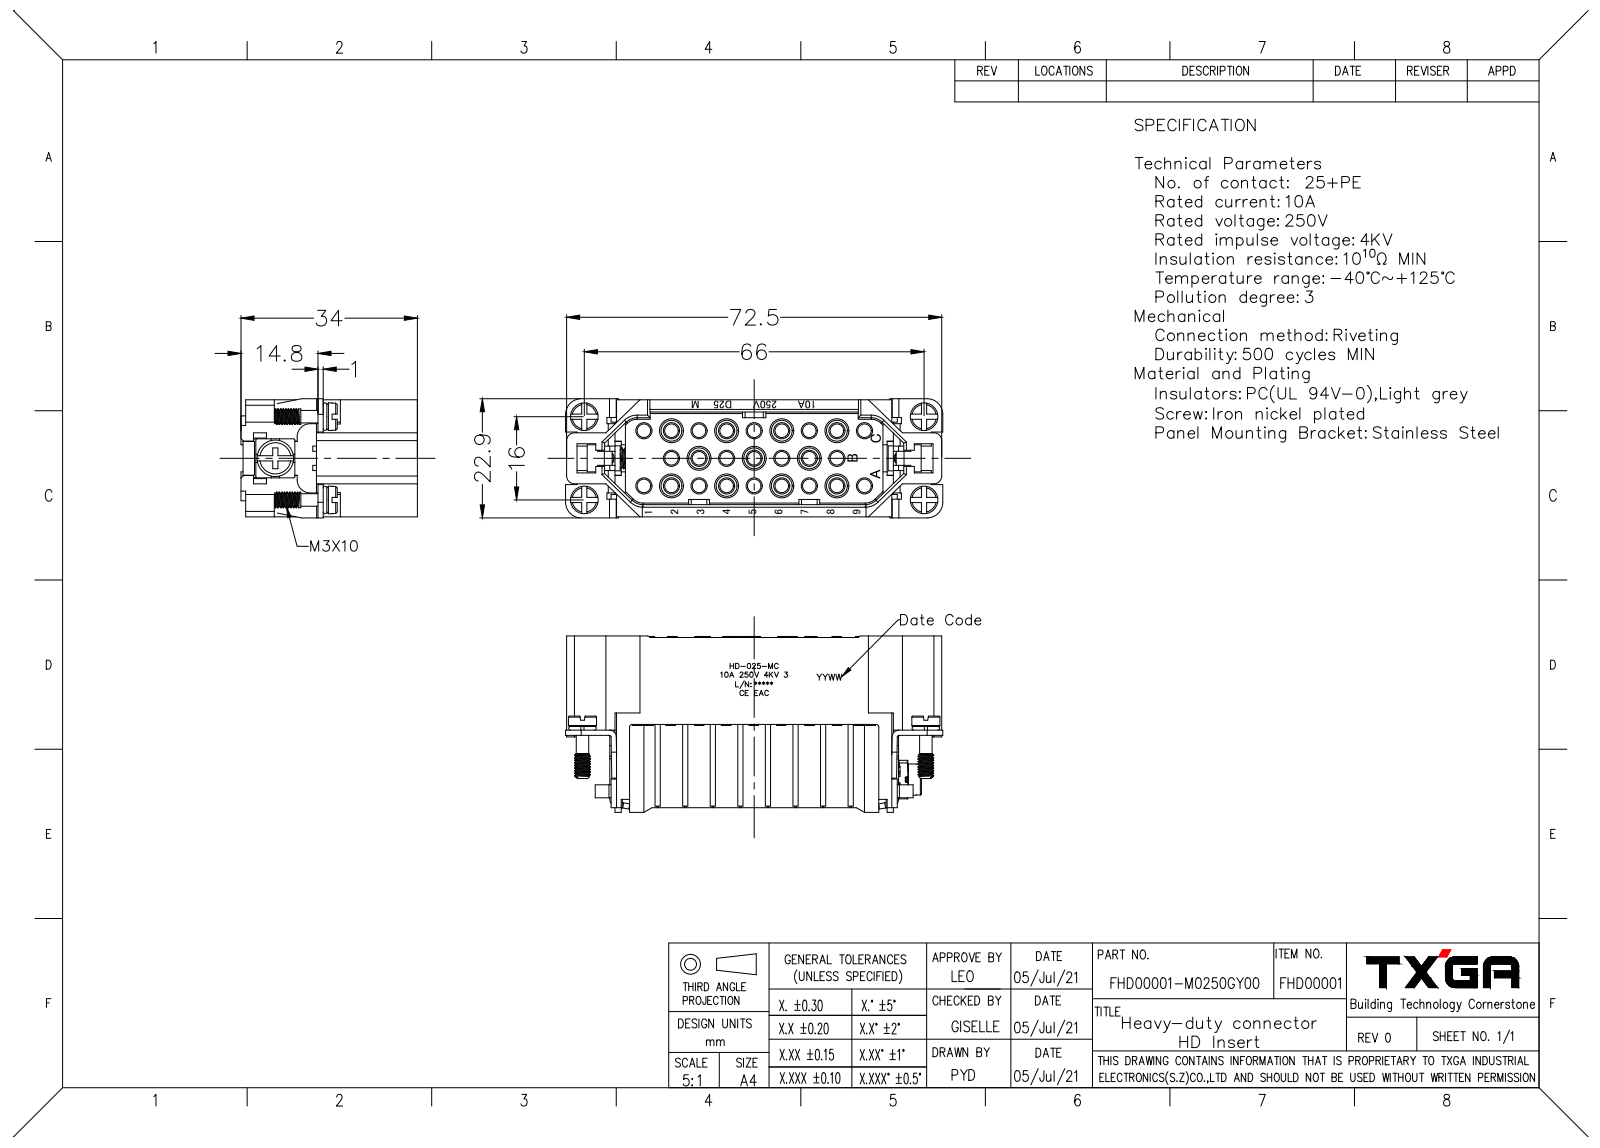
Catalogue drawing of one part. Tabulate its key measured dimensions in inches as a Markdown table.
| quantity | value |
| --- | --- |
| part name | FHD00001-M0250GY00 HD-025-MC-REF（渲染） |
| STEP written by | SolidWorks 2021 (CONFIG_CONTROL_DESIGN) |
| units | inches |
| bodies | 1 solid, 1179 faces (537 planar, 434 cylindrical, 208 other) |
| overall size | 2.854 × 1.339 × 0.902 |
| volume | 1.099 in³ |
| surface area | 35.87 in² |
| round holes (diameter × count) | 0.118 × 29, 0.157 × 29, 0.053 × 12, 0.11 × 1, 0.122 × 1 |
| round bosses / shafts (diameter × count) | 0.236 × 5, 0.102 × 5 |
| partial cylindrical surfaces (radius × count) | 0.02 × 30, 0.008 × 17, 0.039 × 16, 0.096 × 14, 0.079 × 10, 0.047 × 8, 0.118 × 8, 0.1 × 4 |
| main face-to-face distances | 0.039, 0.217, 0.433, 0.65, 0.866, 0.177, 0.689, 0.256, 0.091, 0.61 |
| hole center spacings | 0.217, 0.337, 0.446, 0.433, 0.14, 0.324, 0.548, 0.621 |
